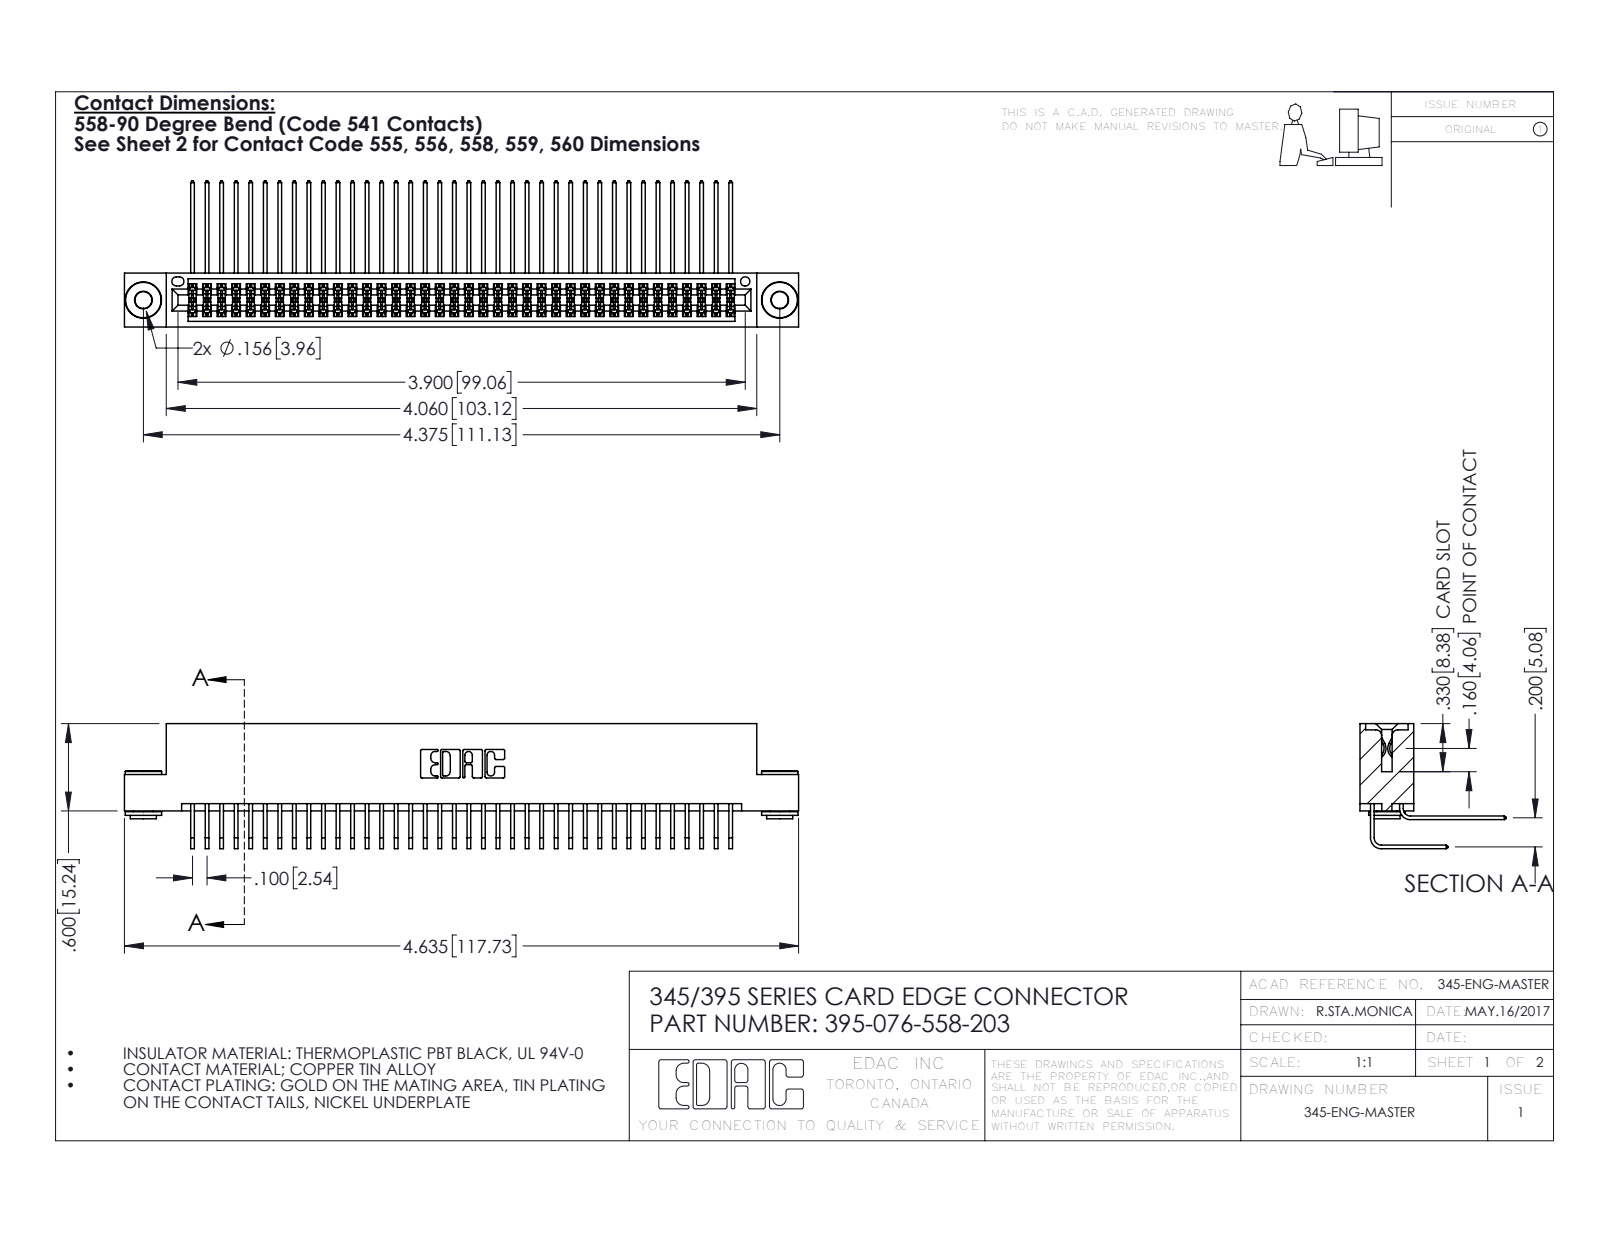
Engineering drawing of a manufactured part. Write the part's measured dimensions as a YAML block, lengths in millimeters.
part_name: "345-292-001_558 559 Tail - 1; 345-250-002_345-250-002-102; 395-076-558-203; 345-292-001_558 Tail - 2 (+1 more)"
step_written_by: "SolidWorks 2016 (CONFIG_CONTROL_DESIGN)"
units: millimeters
bodies: {solids: 79, faces: 4116, planar: 2750, cylindrical: 1358, other: 8}
overall_size: [117.7, 25.5, 21.8]
volume: 11900
surface_area: 19720
round_holes:
  - {diameter: 2.9, count: 2}
  - {diameter: 4, count: 2}
  - {diameter: 1.6, count: 1}
round_bosses_or_shafts:
  - {diameter: 6.4, count: 2}
  - {diameter: 4.6, count: 2}
  - {diameter: 3.5, count: 2}
partial_cylinders:
  - {radius: 0.2, count: 114}
  - {radius: 0.3, count: 22}
  - {radius: 0.2, count: 6}
  - {radius: 0.8, count: 6}
  - {radius: 0.7, count: 3}
  - {radius: 0.4, count: 2}
  - {radius: 0.5, count: 2}
  - {radius: 0.6, count: 2}
face_to_face_distances: [1.8, 7.6, 5.1, 9.4, 0.6, 2.5, 6.9, 5.7, 0.6, 7.2]
hole_center_spacings: [6.9, 105.1, 111.1]
